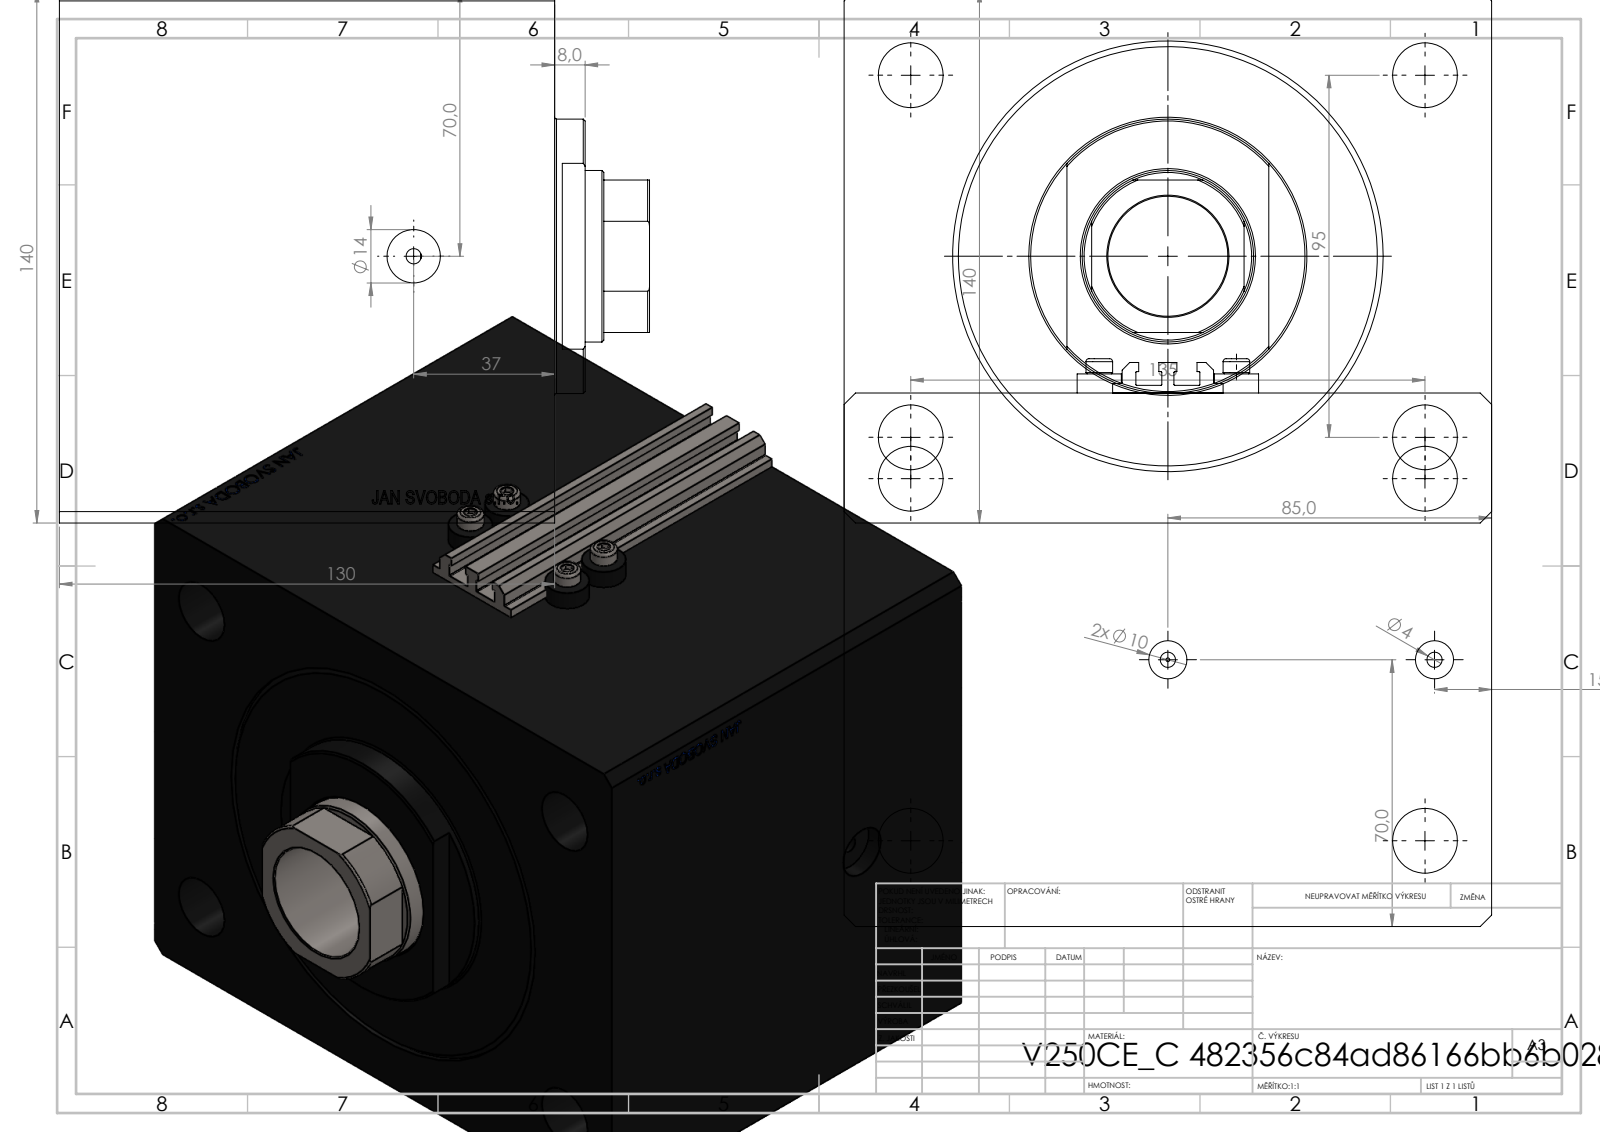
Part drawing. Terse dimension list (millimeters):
name: V250CE_C_Body; ALLEN BOLT V250CE; V250CE_C_VCP; V250CE_VC_C
written by: SolidWorks 2019 (CONFIG_CONTROL_DESIGN)
unit: mm
bodies: 8 solids, 1038 faces (504 planar, 88 cylindrical, 446 other)
size: 170 × 154.9 × 149
volume: 2 868 000 mm³; area: 285 298 mm²
holes: 8× ⌀4, 4× ⌀17, 2× ⌀10, 2× ⌀14, 1× ⌀1.25, 1× ⌀31.5, 1× ⌀45, 1× ⌀100, 1× ⌀113
bosses: 4× ⌀11.6, 4× ⌀7, 1× ⌀72
rounds: 10× R0.2, 1× R22
face distances: 140, 130, 170, 28.9, 101.1, 66, 94.9, 35.1, 20, 74.9
hole spacings: 82.54, 13.6, 36, 38.48, 47.57, 95, 135, 145.47
